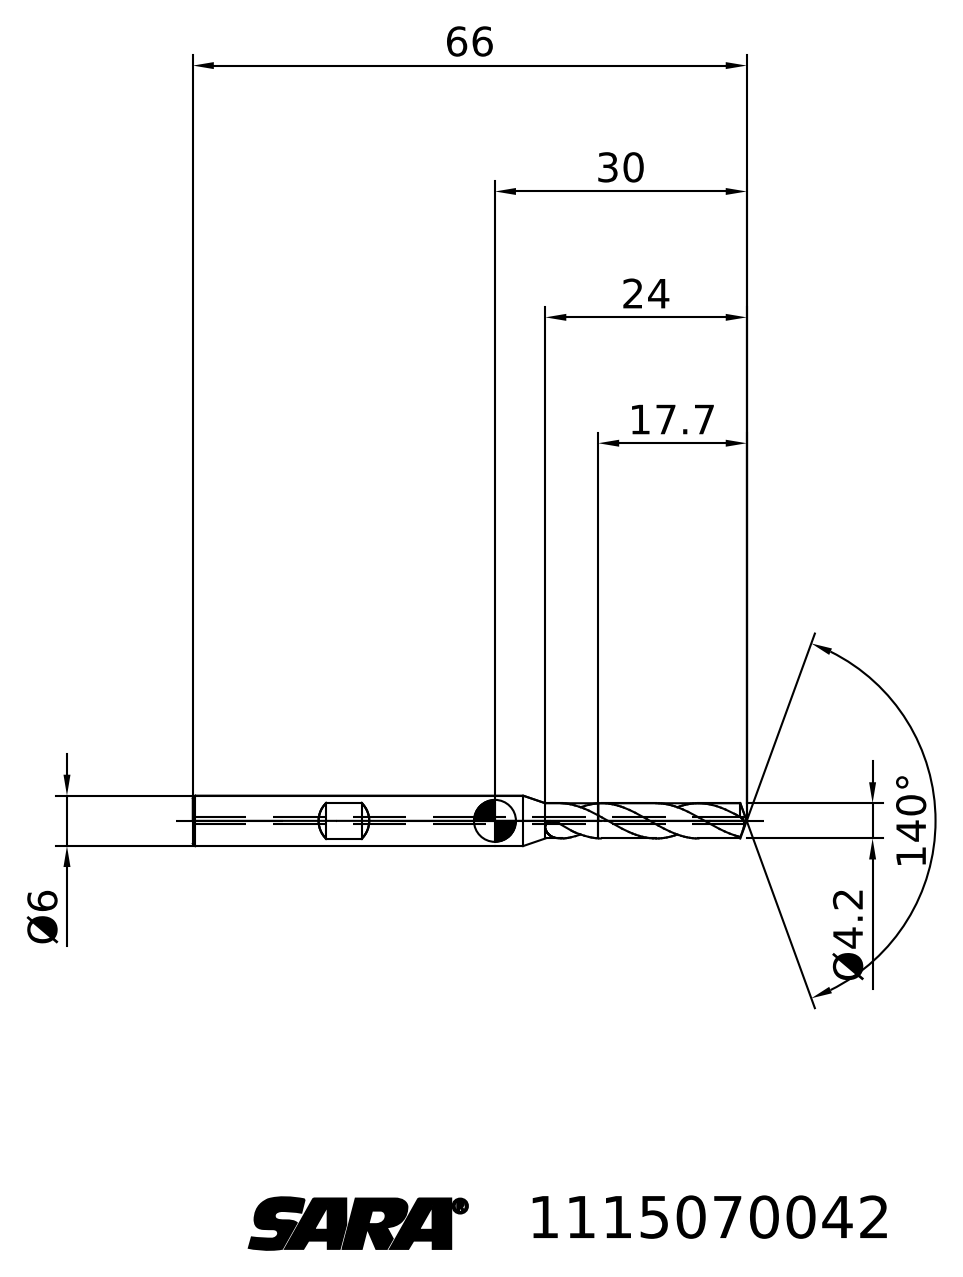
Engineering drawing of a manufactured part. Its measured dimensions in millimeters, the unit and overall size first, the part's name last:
Units: millimetres
Overall size (bounding box): 66 × 6 × 6
Main face-to-face distances: 48.3
Volume: 1 373 mm³ · Surface area: 1 175 mm²
Bodies: 2 solids, 29 faces (6 planar, 0 cylindrical, 23 other)
STEP written by: TDM (AUTOMOTIVE_DESIGN)
